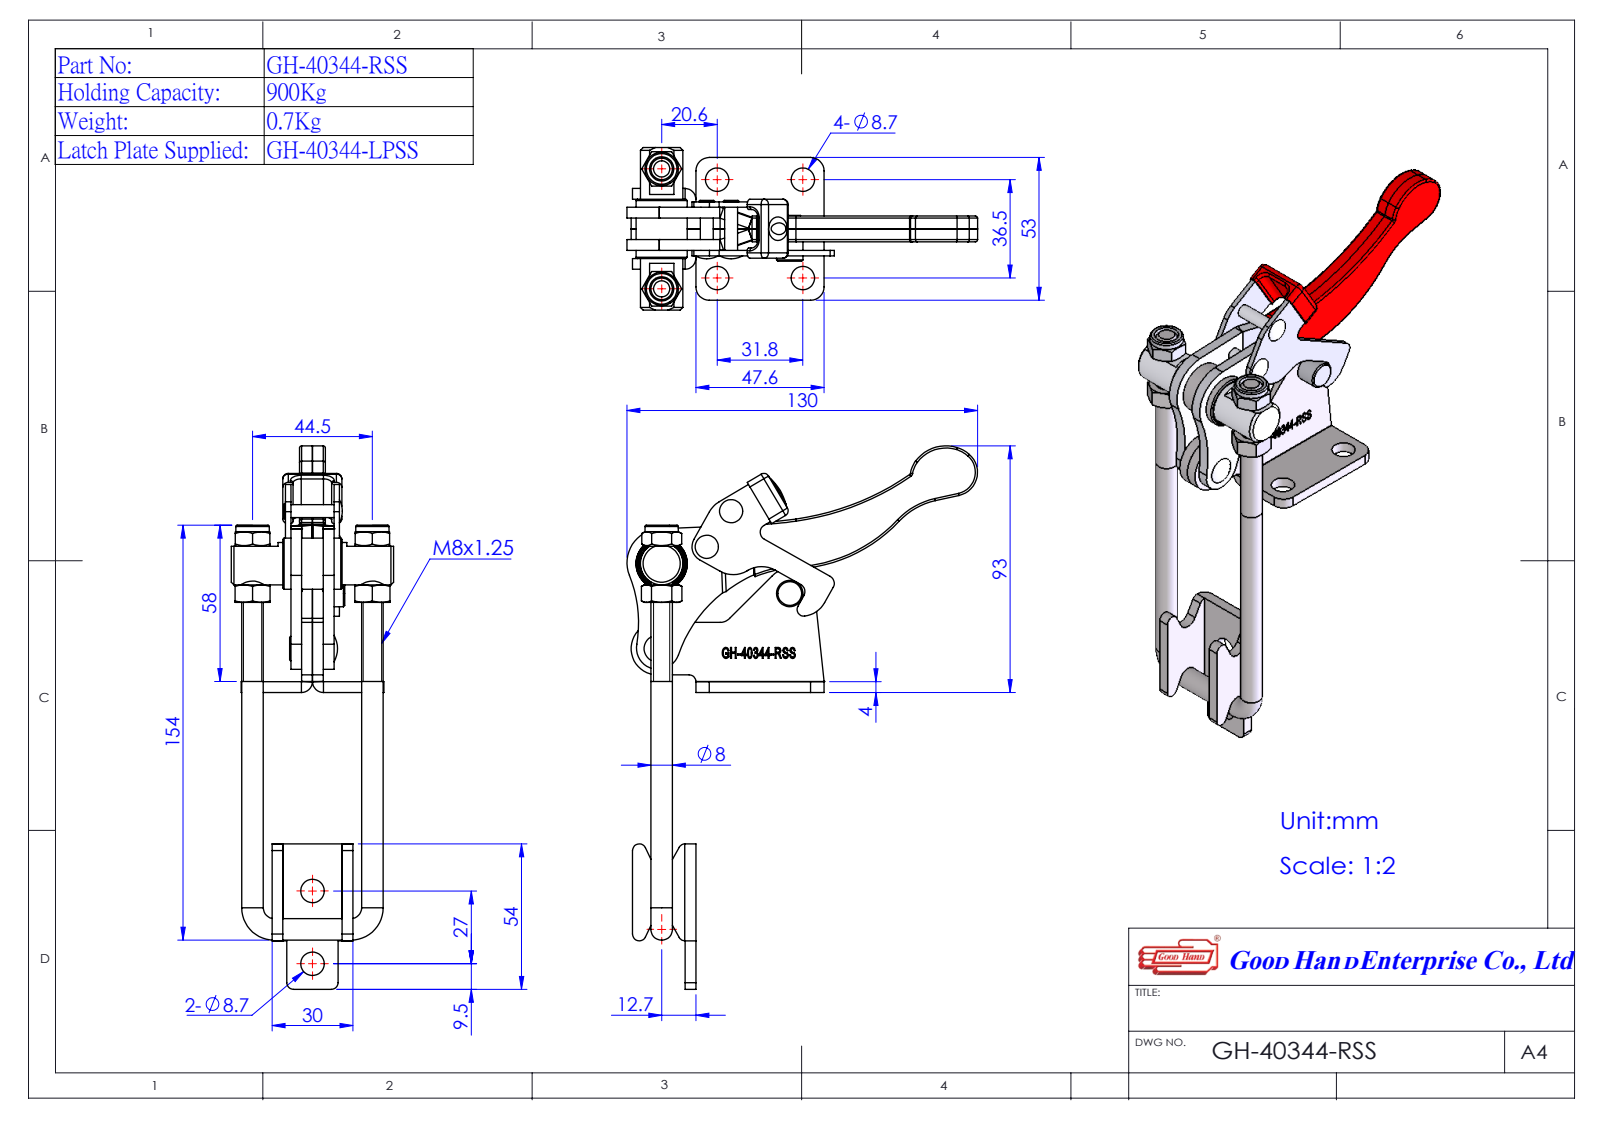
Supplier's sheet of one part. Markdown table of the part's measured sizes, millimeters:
| quantity | value |
| --- | --- |
| part name | 140344SS15-1^GH-40344-RSS; 140344R03(?); GH-40344-RSS; 440344SS44-1^GH-40344-RSS (+3 more) |
| STEP written by | SolidWorks 2016 (AUTOMOTIVE_DESIGN) |
| units | millimeters |
| bodies | 10 solids, 687 faces (317 planar, 174 cylindrical, 196 other) |
| overall size | 203.86 × 129.08 × 60.3 |
| volume | 95 221 mm³ |
| surface area | 51 444 mm² |
| round holes (diameter × count) | 8.7 × 6, 6.8 × 2, 8.5 × 2, 9 × 2, 1.91 × 1, 4 × 1, 6 × 1, 6.3 × 1, 16 × 1 |
| round bosses / shafts (diameter × count) | 8 × 3, 12.4 × 2, 15.77 × 1, 9.8 × 1, 6 × 1, 5.92 × 1, 1.83 × 1 |
| partial cylindrical surfaces (radius × count) | 3 × 7, 5 × 7, 2.5 × 6, 0.1 × 5, 7 × 4, 10 × 4, 0.73 × 3, 0.77 × 3 |
| main face-to-face distances | 4, 3, 1, 12, 13, 9, 16, 8, 6, 15 |
| hole center spacings | 0.84, 20.98, 21.81, 31.8, 36.5, 44.5, 44.51, 45.44 |
